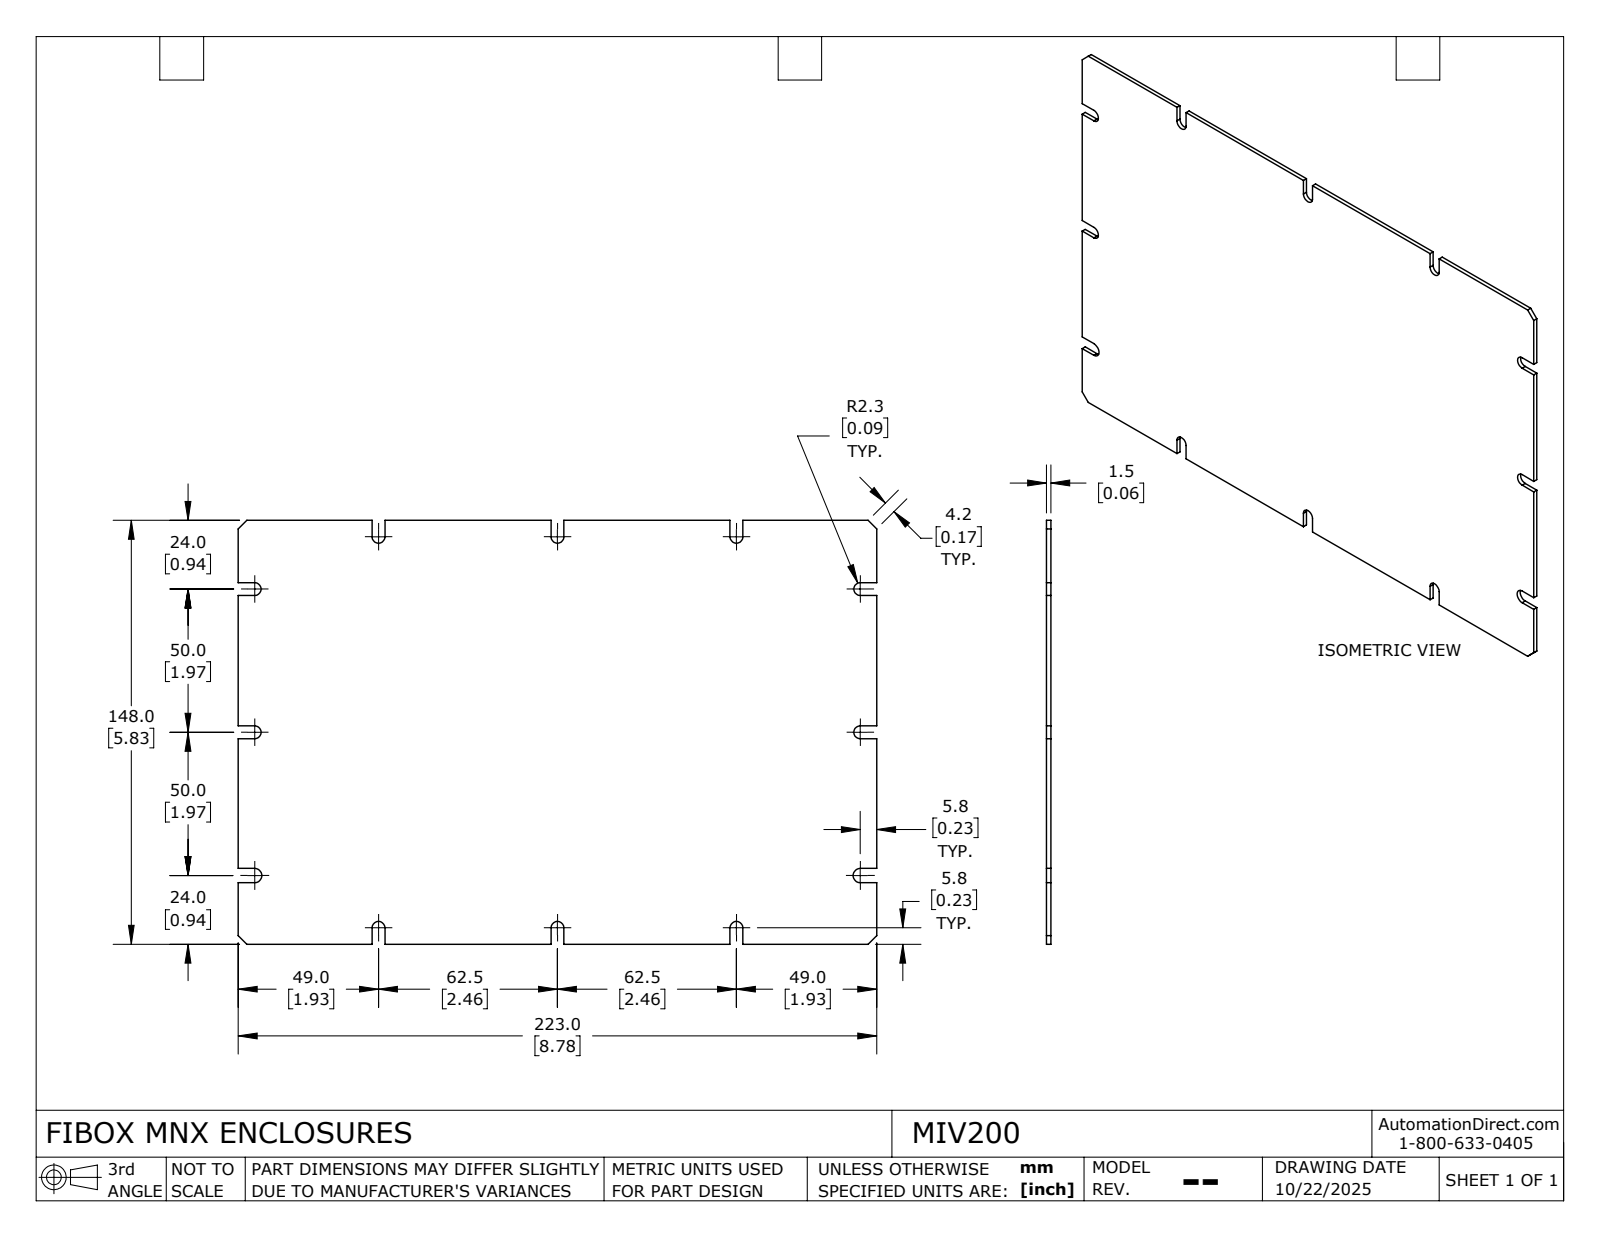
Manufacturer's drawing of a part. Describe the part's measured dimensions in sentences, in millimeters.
The part is named "MIV200_Default". Its 3-D file was written by "SolidWorks 2024 (CONFIG_CONTROL_DESIGN)". It is 1 solid with 58 faces: 46 planar, 12 cylindrical and 0 other. Overall it measures 223 by 148 by 1.5 millimeters. Its volume is 48 856 cubic millimeters and its surface area 66 498 square millimeters. Partial cylindrical surfaces (rounded edges, fillets, slot ends): 10 of radius 2.25, 2 of radius 2.5. The main face-to-face distances are 1.5, 148, 223, 4.5, 62.5, 71.75, 76.25, 50, 46.75, 51.25.
